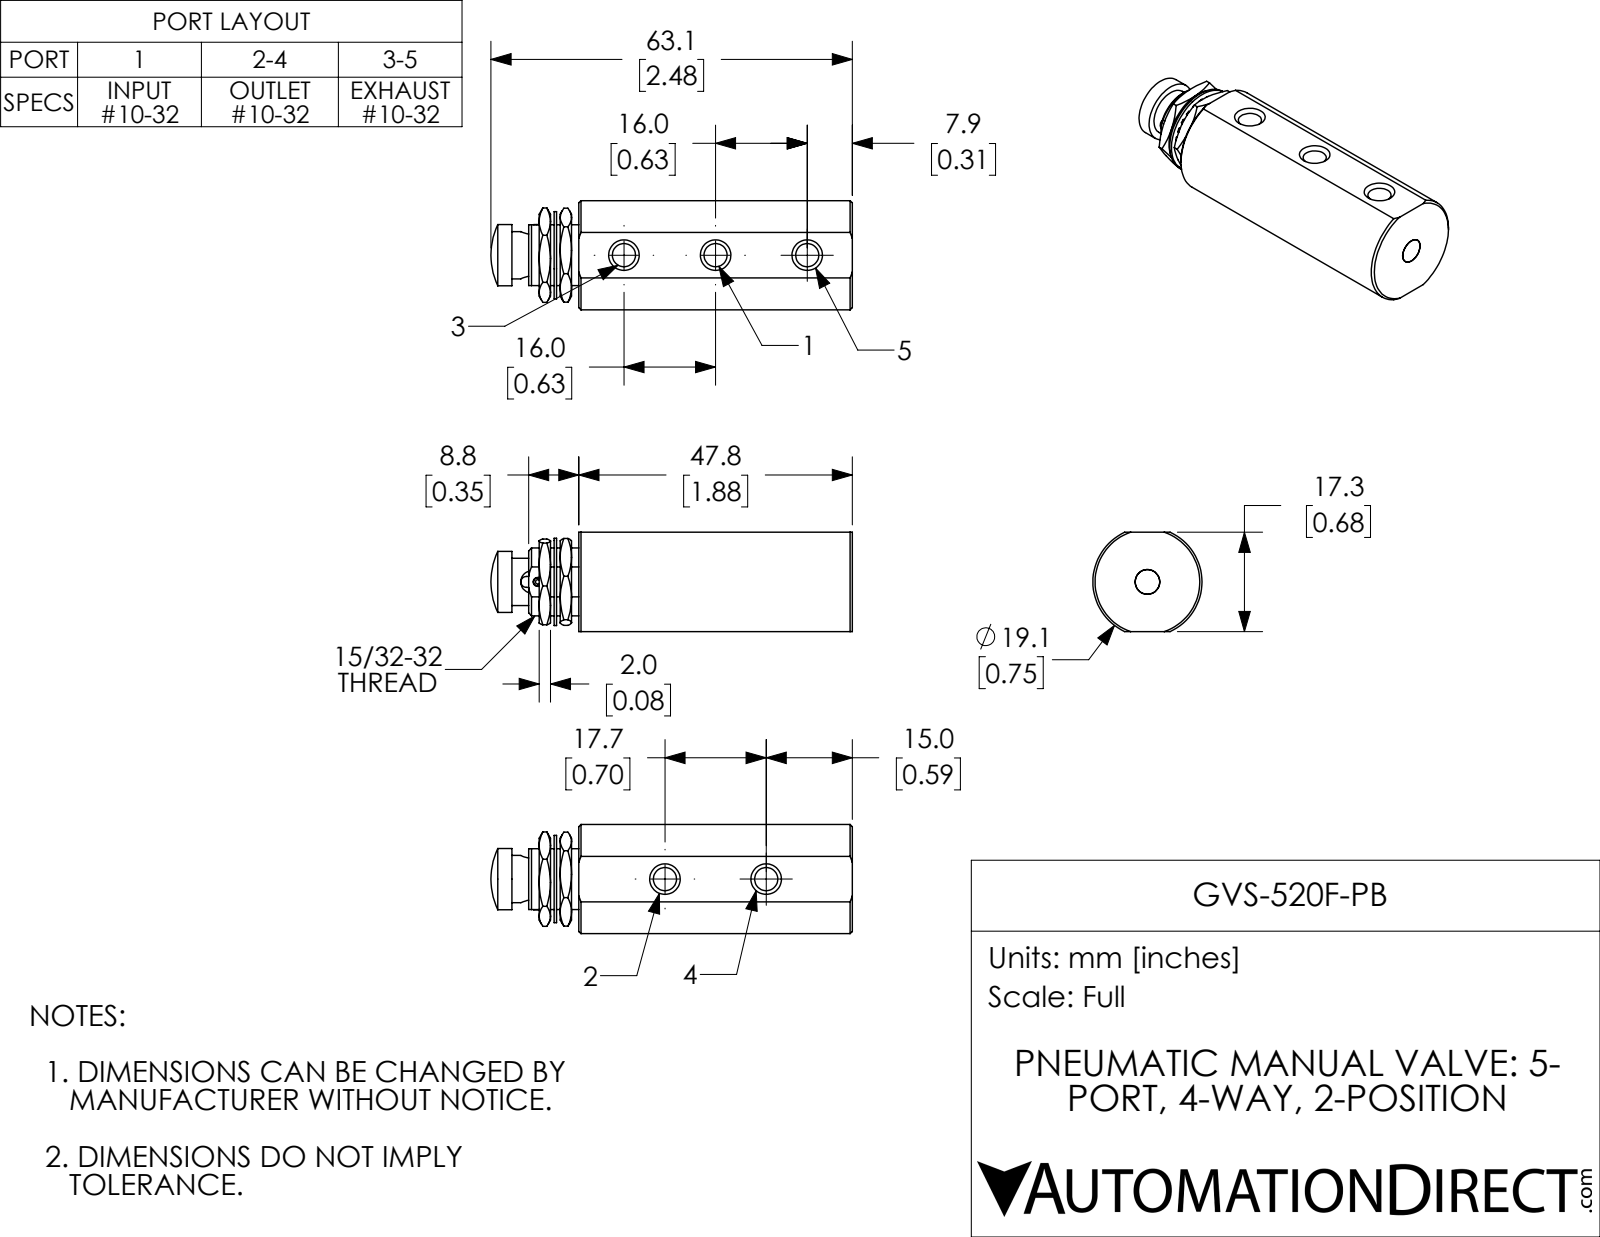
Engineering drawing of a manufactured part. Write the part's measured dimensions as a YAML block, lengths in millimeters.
part_name: "GVS-520F-PB"
step_written_by: "SolidWorks 2018 (AUTOMOTIVE_DESIGN)"
units: millimeters
bodies: {solids: 7, faces: 273, planar: 101, cylindrical: 106, other: 66}
overall_size: [63.1, 19.1, 17.3]
volume: 11300
surface_area: 6987
round_holes:
  - {diameter: 4, count: 5}
  - {diameter: 0.8, count: 1}
  - {diameter: 1.6, count: 1}
  - {diameter: 3.9, count: 1}
  - {diameter: 4.3, count: 1}
  - {diameter: 4.6, count: 1}
  - {diameter: 7.4, count: 1}
  - {diameter: 8.4, count: 1}
  - {diameter: 10.5, count: 1}
  - {diameter: 11.1, count: 1}
round_bosses_or_shafts:
  - {diameter: 15.2, count: 1}
  - {diameter: 10.7, count: 1}
  - {diameter: 8.3, count: 1}
  - {diameter: 1.6, count: 1}
partial_cylinders:
  - {radius: 0.9, count: 2}
  - {radius: 5.9, count: 1}
  - {radius: 6.1, count: 1}
  - {radius: 6.6, count: 1}
  - {radius: 9.5, count: 1}
face_to_face_distances: [17.3, 3.9, 43.8, 47.8, 26.3, 3.7, 2, 1.7, 17.5, 30.2]
hole_center_spacings: [7.2, 8.8, 16, 24.8, 1, 17.7, 32]
